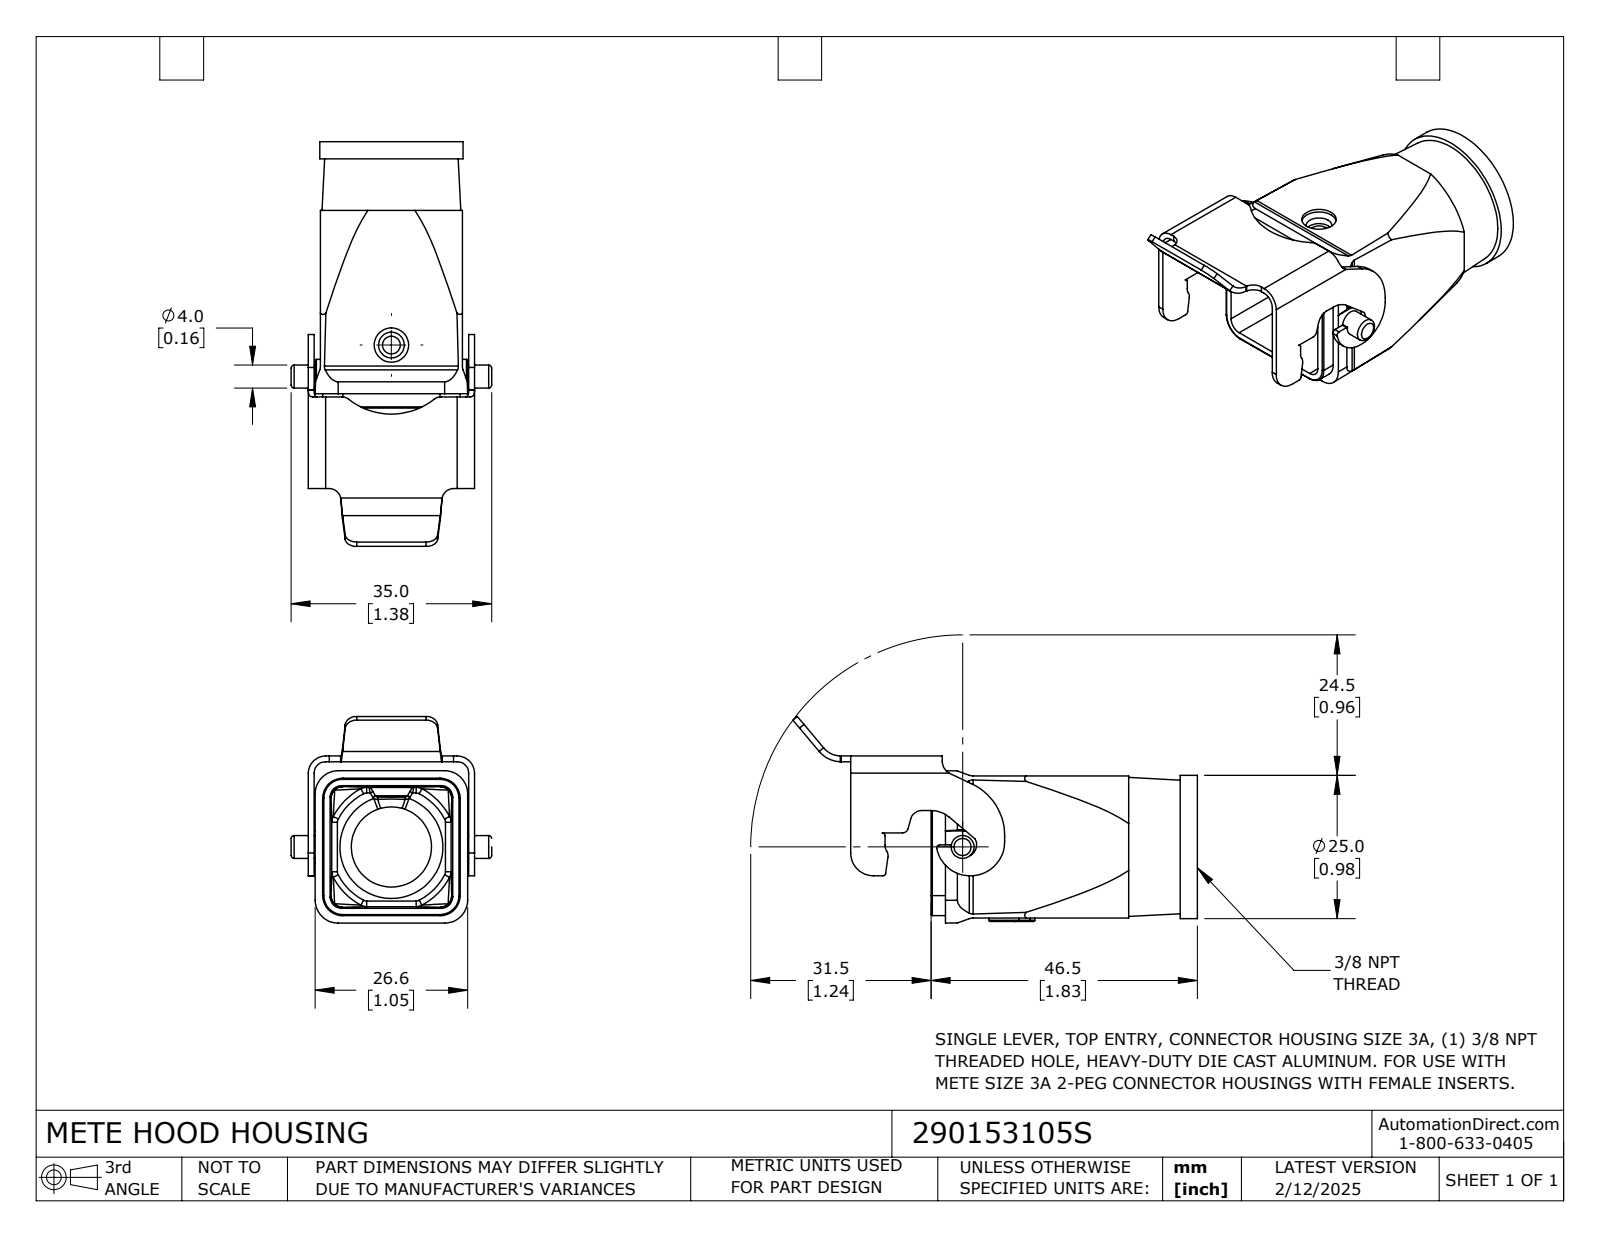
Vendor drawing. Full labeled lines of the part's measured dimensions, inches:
Part name (STEP PRODUCT): 290153105S
STEP written by: SolidWorks 2024 (CONFIG_CONTROL_DESIGN)
Units: inches
Bodies: 1 solid, 306 faces (111 planar, 122 cylindrical, 73 other)
Overall size (bounding box): 2.781 × 1.421 × 1.378
Volume: 0.659 in³ · Surface area: 17.66 in²
Round holes (diameter × count): ⌀0.122 ×1, ⌀0.177 ×1, ⌀0.236 ×1, ⌀0.551 ×1, ⌀0.669 ×1
Round bosses / shafts (diameter × count): ⌀0.984 ×1, ⌀0.157 ×1
Partial cylindrical surfaces — rounded edges, fillets, slot ends (radius × count): R0.008 ×25, R0.079 ×17, R0.02 ×11, R0.039 ×5, R0.138 ×4, R0.118 ×3, R0.083 ×2, R0.157 ×2
Main face-to-face distances: 0.039, 0.976, 0.083, 1.059, 0.044, 1.019, 1.102, 1.073, 0.098, 1.113
